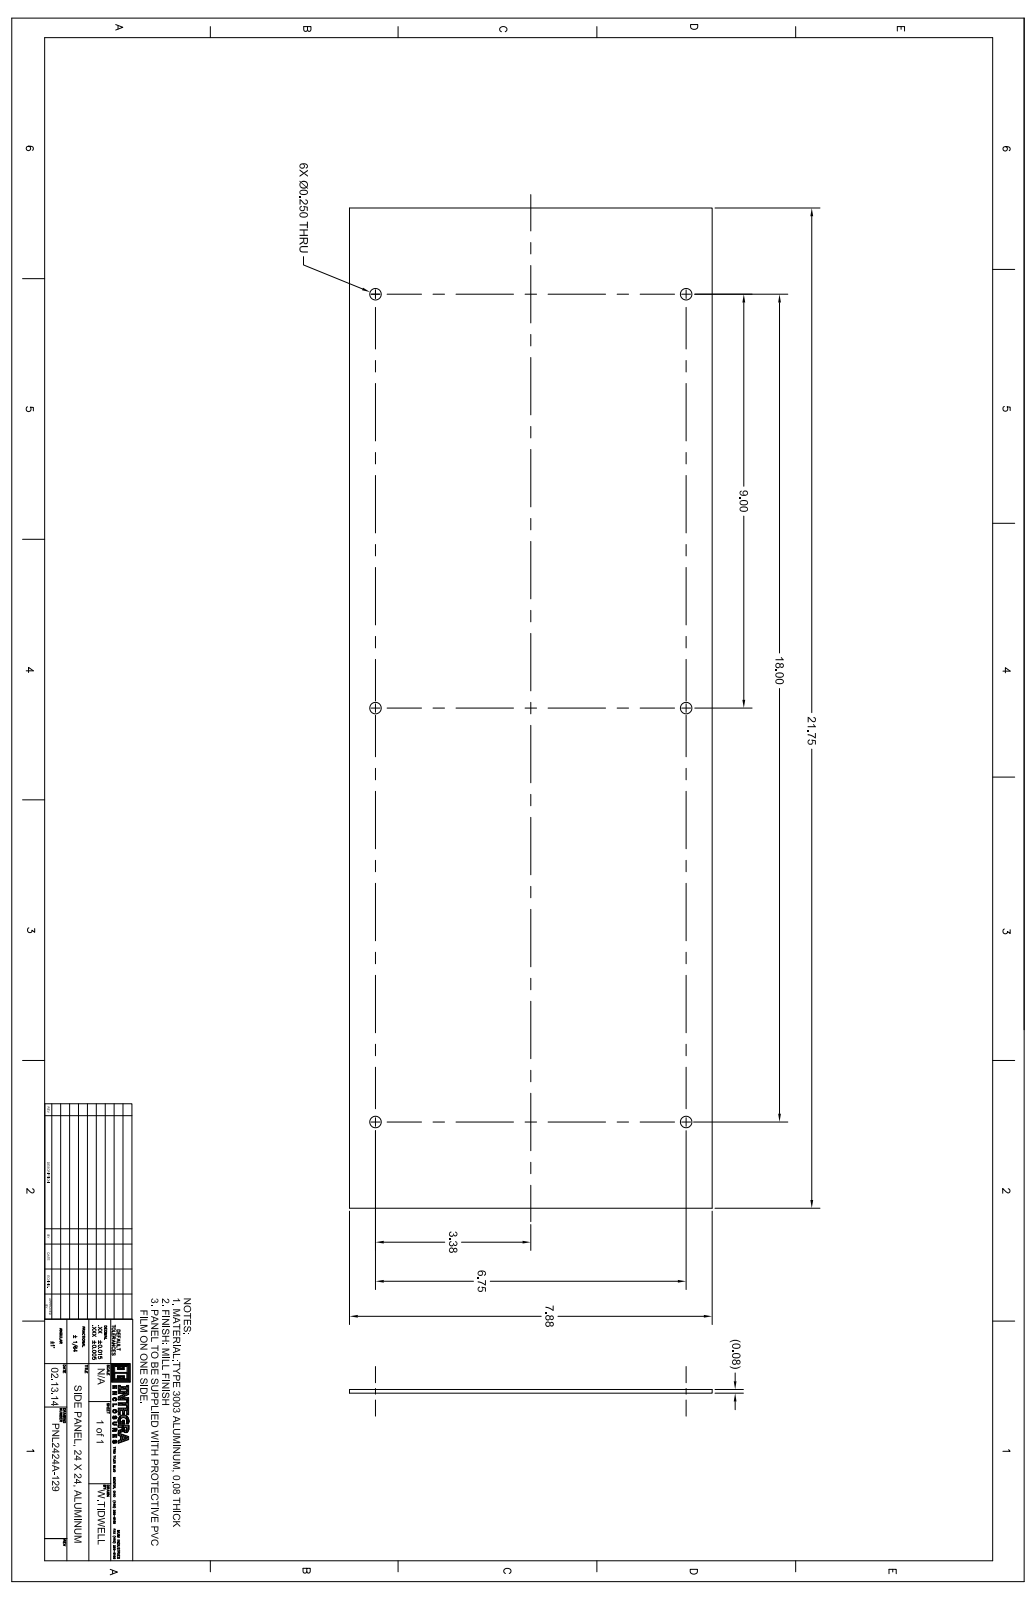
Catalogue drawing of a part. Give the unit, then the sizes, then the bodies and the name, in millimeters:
Units: millimetres
Overall size (bounding box): 552.5 × 200 × 2
Round holes (diameter × count): ⌀6.4 ×6
Main face-to-face distances: 2, 200, 552.5
Hole centre spacings: 228.6, 285.8, 171.5, 457.2, 488.3
Volume: 224 200 mm³ · Surface area: 223 900 mm²
Bodies: 1 solid, 12 faces (6 planar, 6 cylindrical, 0 other)
Part name (STEP PRODUCT): ASP-2424-P10
STEP written by: SolidWorks 2018 (AUTOMOTIVE_DESIGN)
